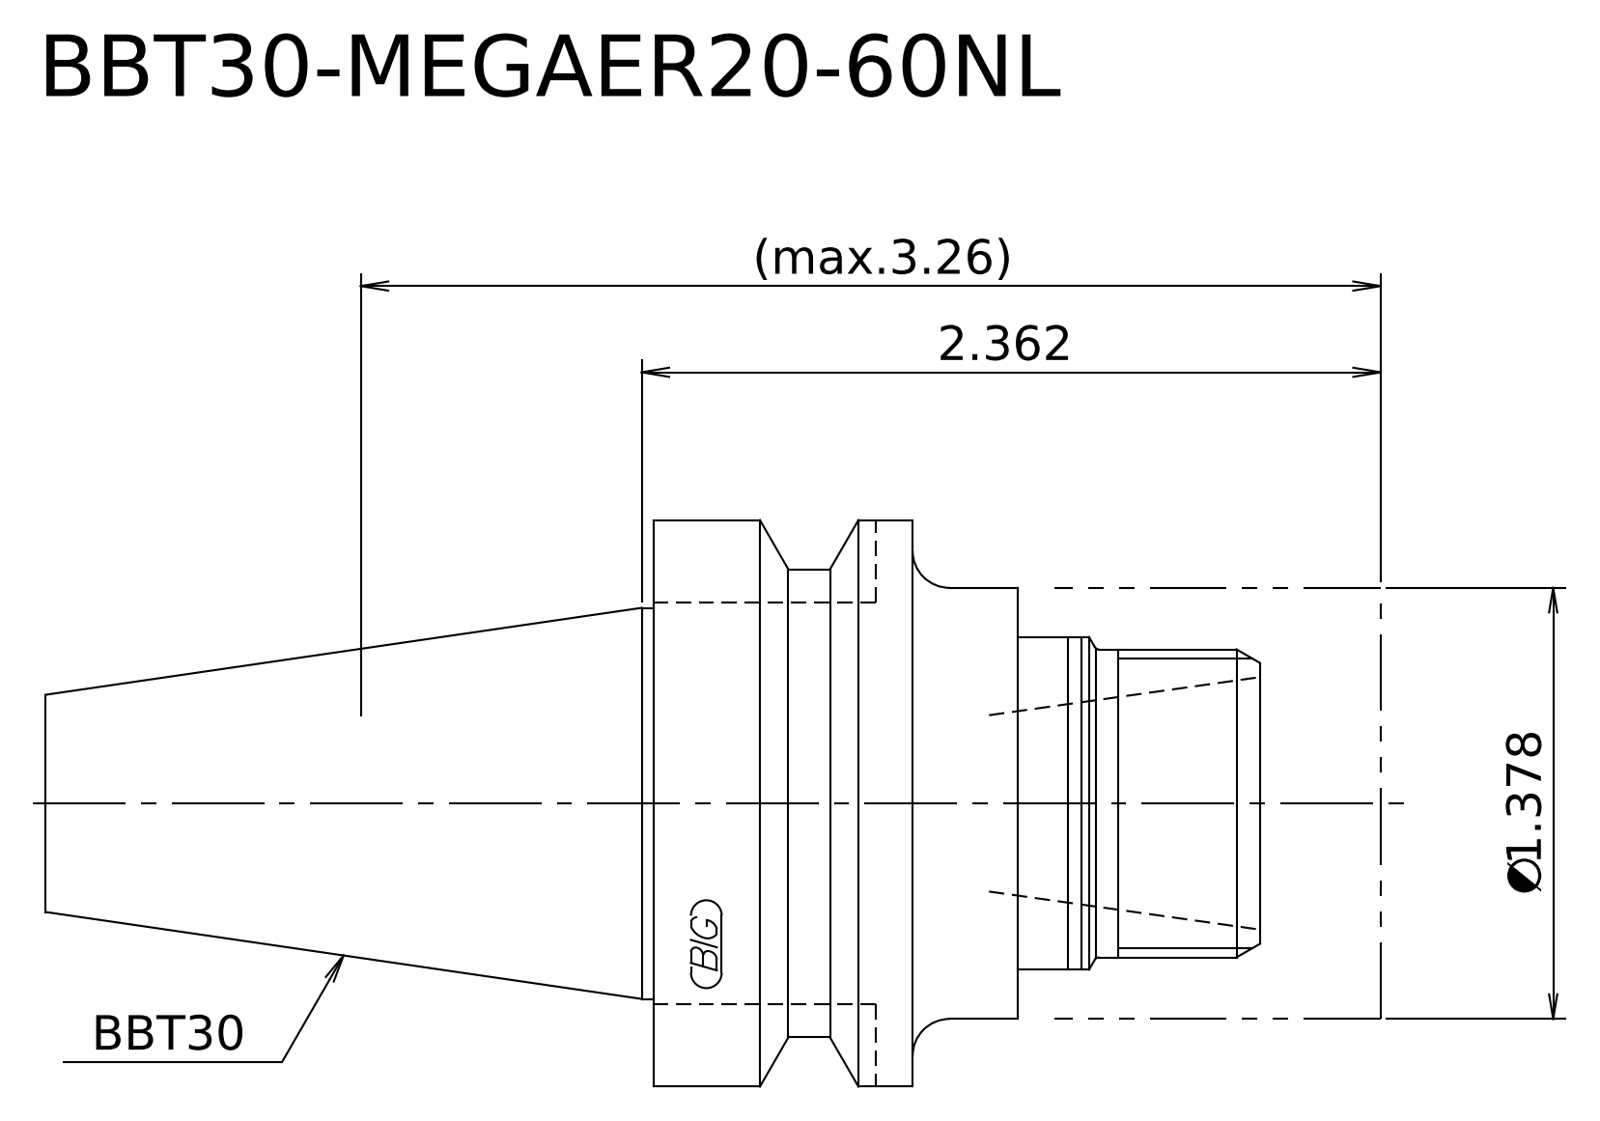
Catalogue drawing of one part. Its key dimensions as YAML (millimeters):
step_written_by: "Kubotek KeyCreator 2011 V10.0.2 (22737) (automotive_design)"
units: millimeters
bodies: {solids: 2, faces: 21, planar: 7, cylindrical: 8, other: 6}
overall_size: [108.4, 46, 46]
volume: 100743
surface_area: 17247
round_bosses_or_shafts:
  - {diameter: 46, count: 1}
  - {diameter: 38, count: 1}
  - {diameter: 35, count: 1}
  - {diameter: 31.75, count: 1}
  - {diameter: 27, count: 1}
  - {diameter: 25, count: 1}
face_to_face_distances: [26.5, 59, 32.5, 29.5, 9.8, 16.7, 49.2, 19.7, 3, 38]
